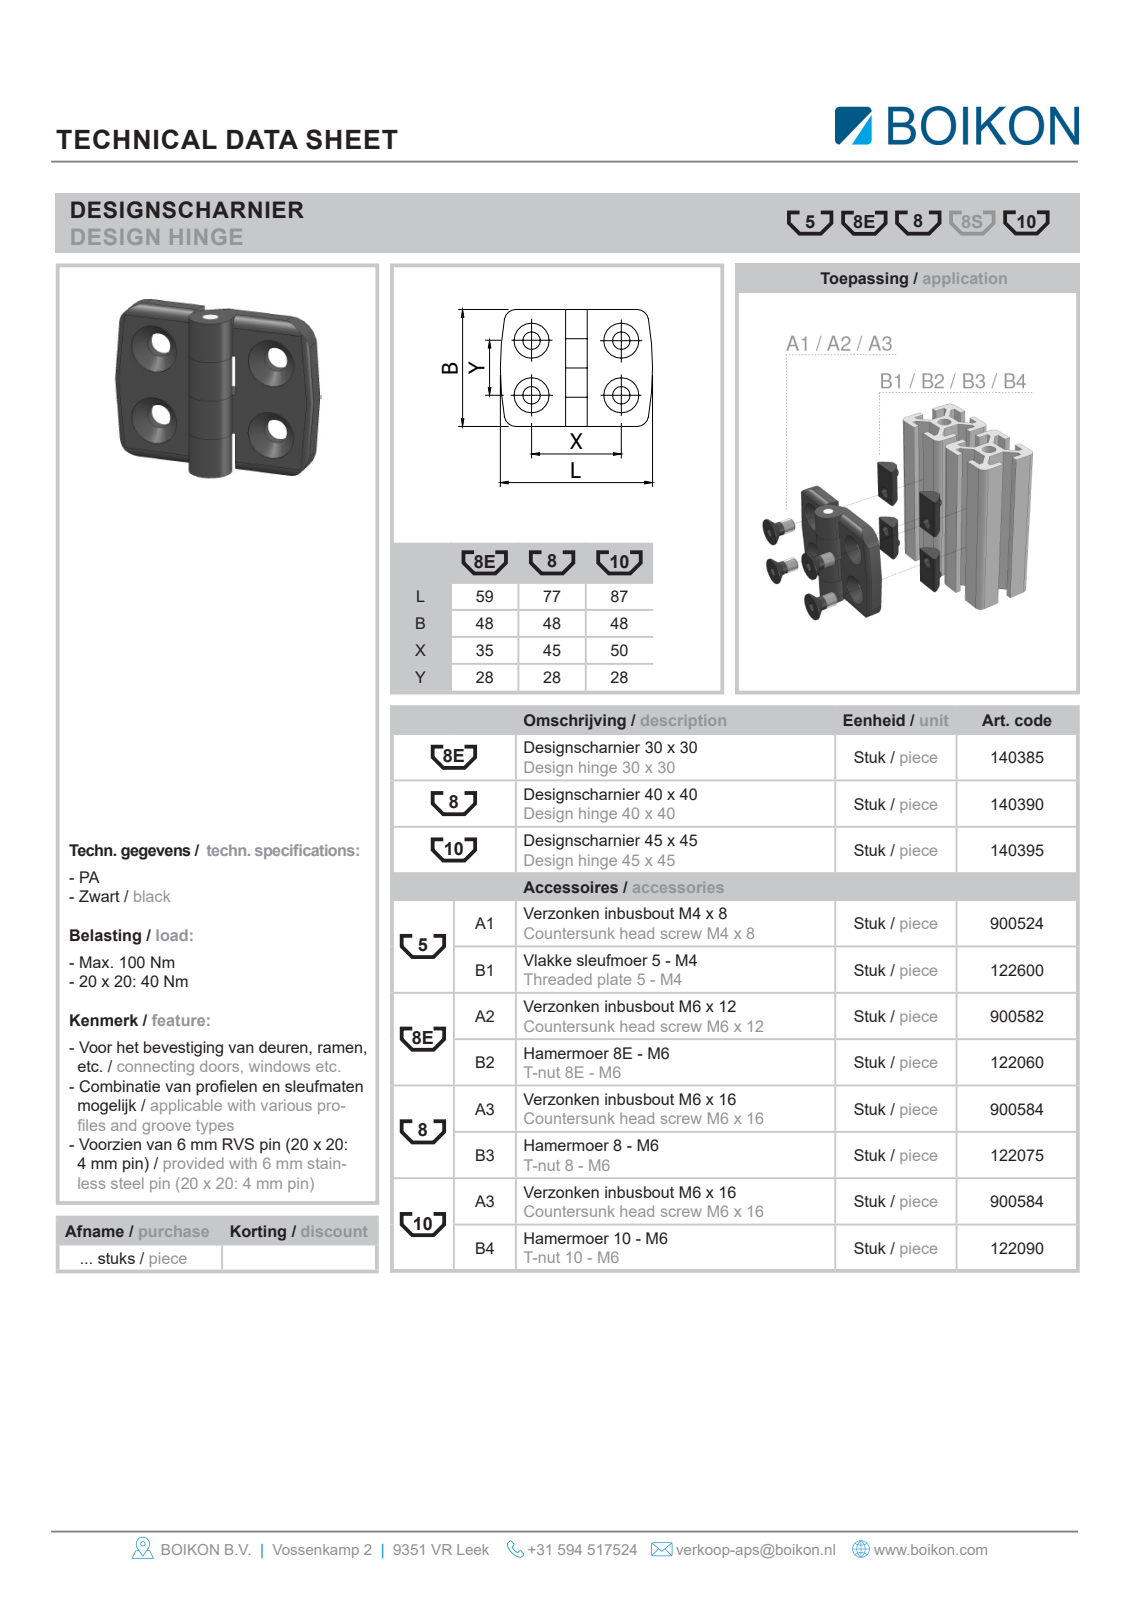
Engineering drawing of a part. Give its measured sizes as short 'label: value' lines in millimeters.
name: Root; 140385Scharnier met RVS pen 30x30BOIKON
written by: HiCAD 2013 1802.4 Build 509 (AUTOMOTIVE_DESIGN)
unit: mm
bodies: 3 solids, 61 faces (28 planar, 27 cylindrical, 6 other)
size: 59 × 48 × 15.9
volume: 22 231 mm³; area: 11 097 mm²
holes: 4× ⌀6.6, 4× ⌀13, 1× ⌀6
bosses: 1× ⌀14
rounds: 4× R6, 2× R4, 2× R100
face distances: 12, 7.9, 24, 36, 48, 14
hole spacings: 28, 35, 44.82
